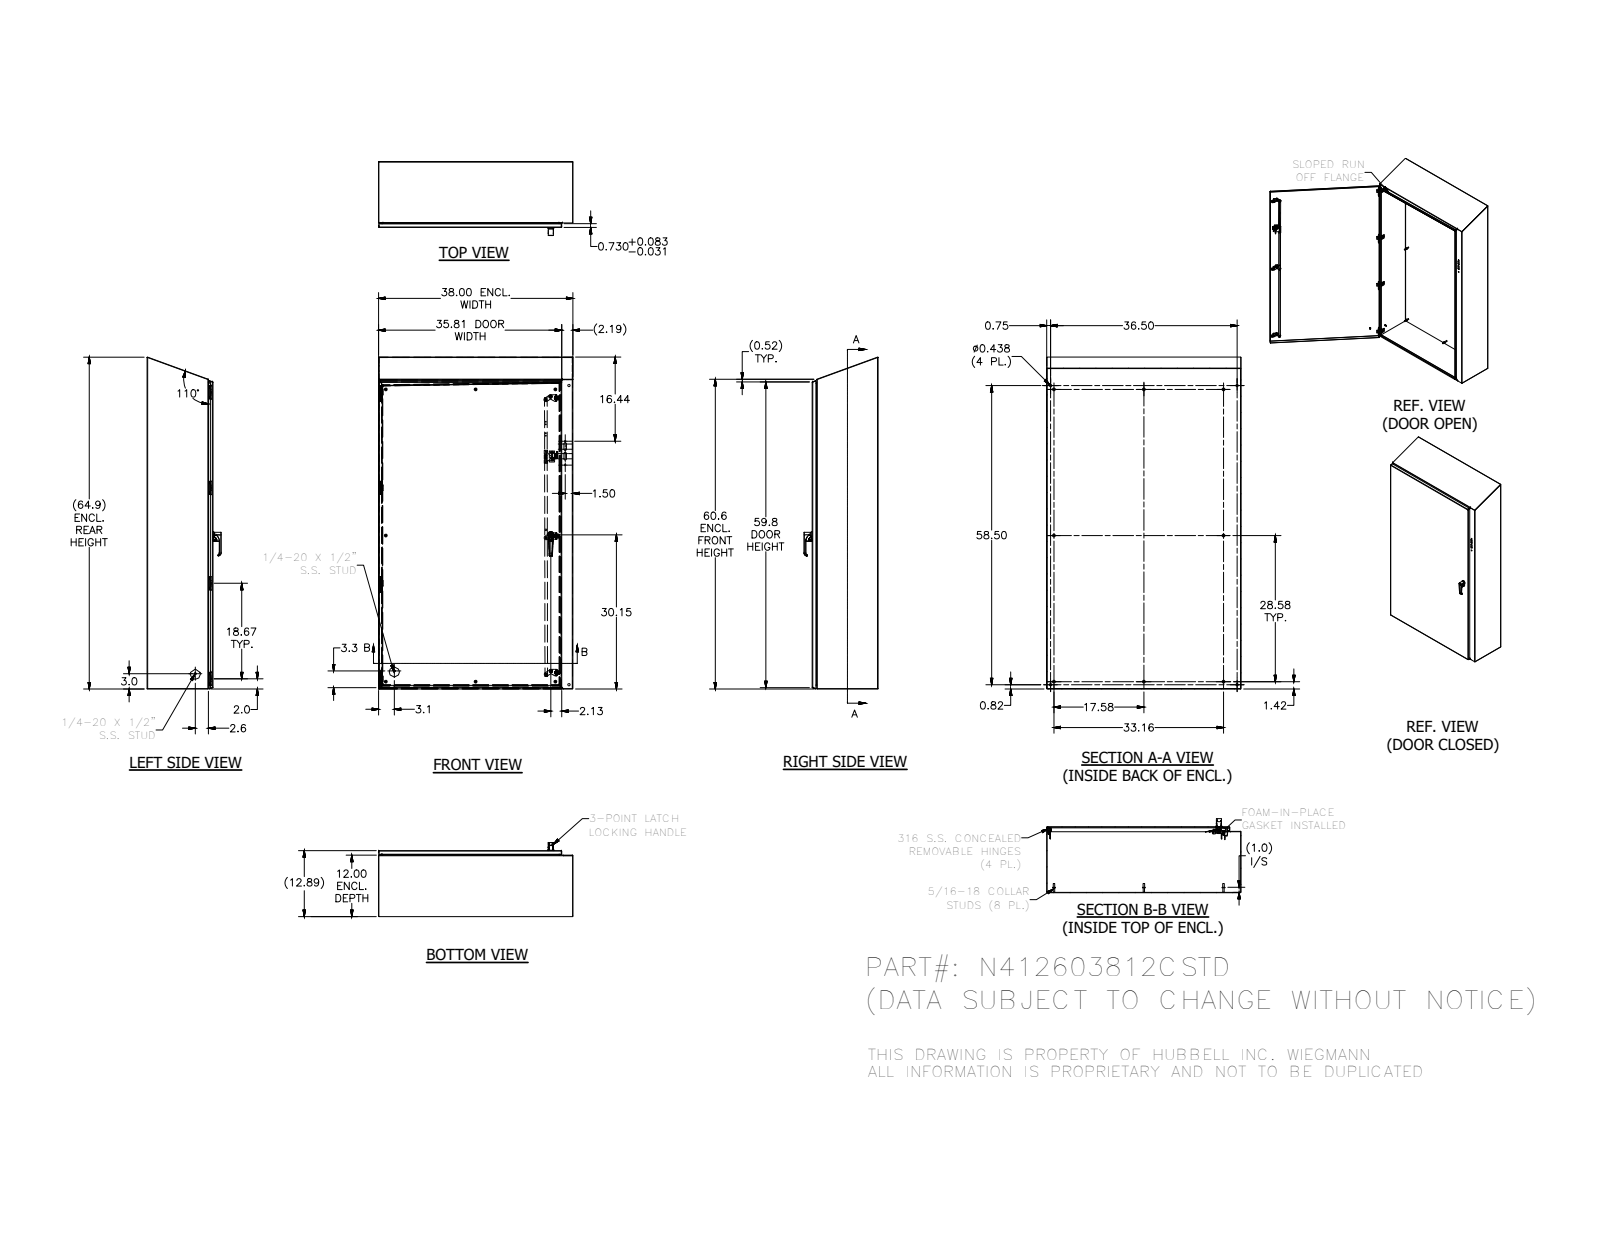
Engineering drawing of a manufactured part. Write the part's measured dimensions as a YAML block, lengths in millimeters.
part_name: "N412603812CSTDBLR; 388150; N4123812CSTDTOP; 38846 (+8 more)"
step_written_by: "Autodesk Inventor 2014 (AUTOMOTIVE_DESIGN)"
units: millimeters
bodies: {solids: 93, faces: 3129, planar: 1174, cylindrical: 1143, other: 812}
overall_size: [1648.35, 965.2, 367.82]
volume: 9384000
surface_area: 9931000
round_holes:
  - {diameter: 2.36, count: 8}
  - {diameter: 3.86, count: 8}
  - {diameter: 4.25, count: 8}
  - {diameter: 4.37, count: 8}
  - {diameter: 4.76, count: 8}
  - {diameter: 3.96, count: 7}
  - {diameter: 3.68, count: 6}
  - {diameter: 8.13, count: 4}
  - {diameter: 11.11, count: 4}
  - {diameter: 4.98, count: 3}
  - {diameter: 5.36, count: 3}
  - {diameter: 5.59, count: 3}
round_bosses_or_shafts:
  - {diameter: 6.35, count: 20}
  - {diameter: 7.62, count: 14}
  - {diameter: 14.3, count: 8}
  - {diameter: 9.14, count: 8}
  - {diameter: 8.13, count: 8}
  - {diameter: 6.99, count: 8}
  - {diameter: 6.5, count: 8}
  - {diameter: 4.17, count: 8}
partial_cylinders:
  - {radius: 1.27, count: 50}
  - {radius: 3.17, count: 45}
  - {radius: 0.5, count: 38}
  - {radius: 0.79, count: 36}
  - {radius: 0.4, count: 34}
  - {radius: 0.3, count: 30}
  - {radius: 0.64, count: 24}
  - {radius: 2.67, count: 18}
face_to_face_distances: [1.88, 325.44, 323.56, 327.32, 963.32, 965.2, 961.44, 302.92, 22.52, 20.64]
hole_center_spacings: [474.13, 474.14, 948.27, 1422.4, 685.8, 948.26, 12.7, 16.66]
